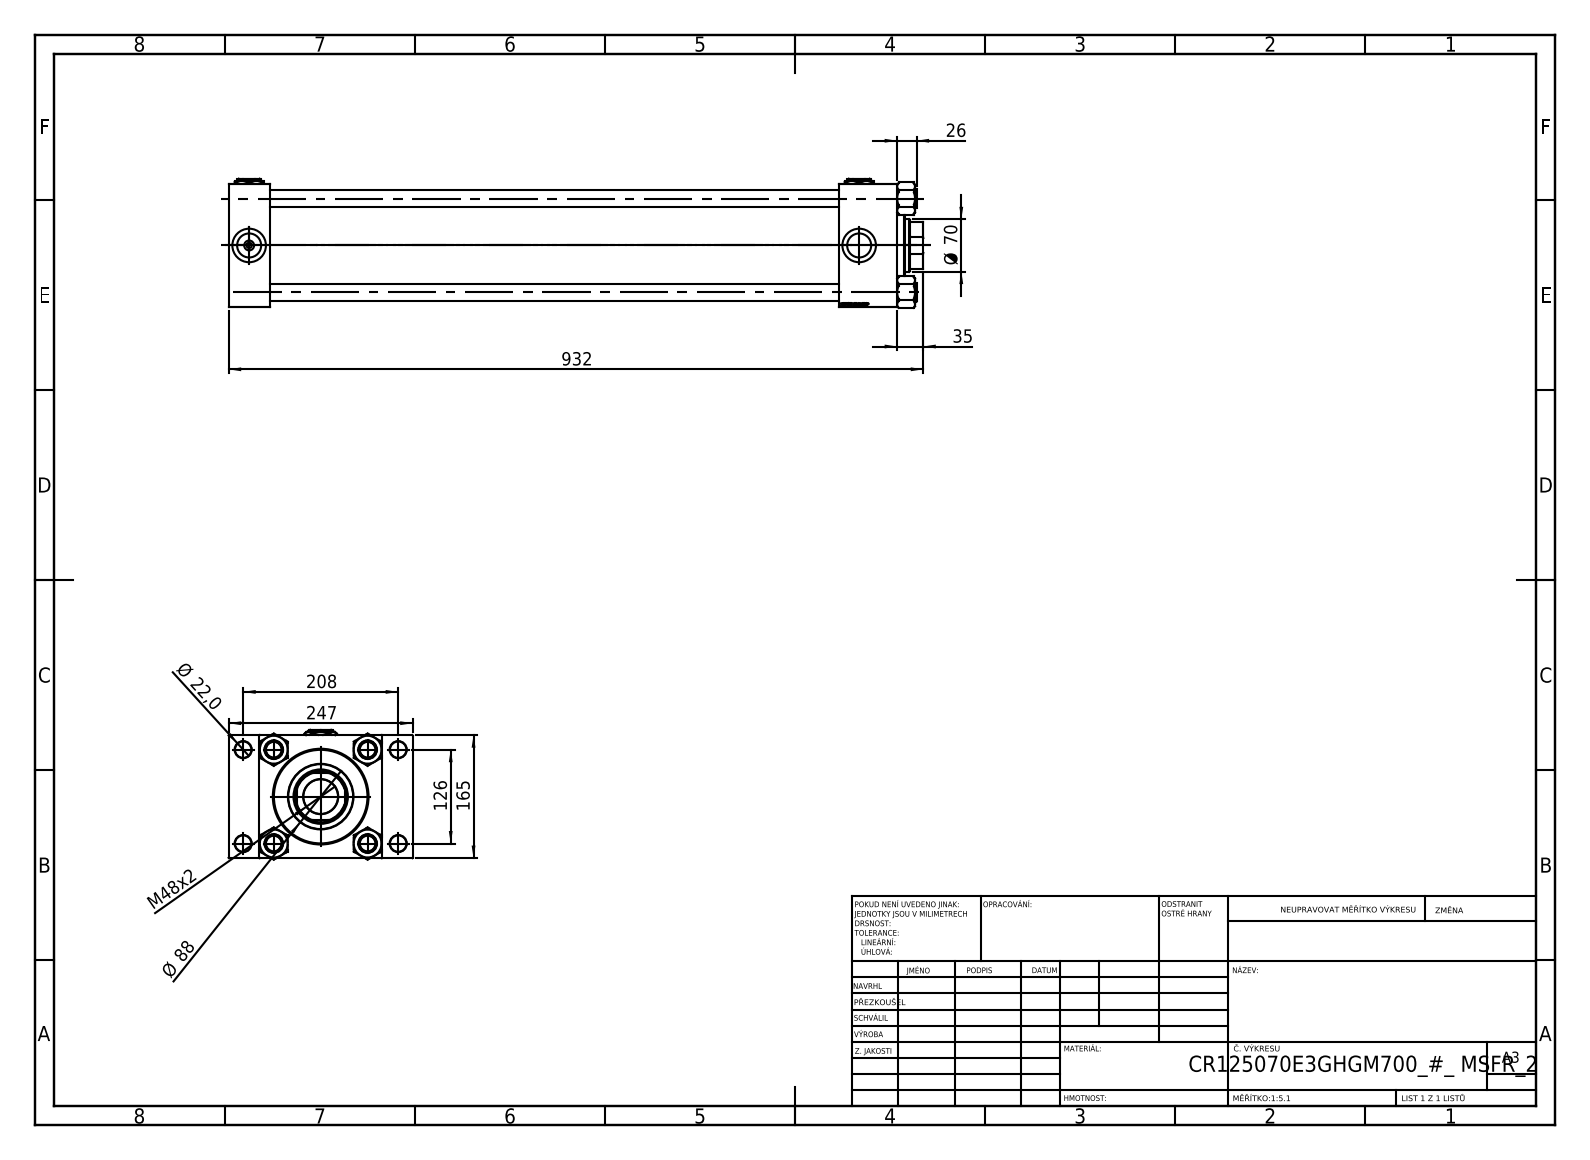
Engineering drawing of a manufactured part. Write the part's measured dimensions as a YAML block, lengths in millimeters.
part_name: "V215CR_VCP_E; V215CR_TYCINKA_E; NUT_M5_E; V215_VC_A (+2 more)"
step_written_by: "SolidWorks 2019 (CONFIG_CONTROL_DESIGN)"
units: millimeters
bodies: {solids: 13, faces: 1284, planar: 593, cylindrical: 97, other: 594}
overall_size: [932, 247, 174.07]
volume: 9729000
surface_area: 1475000
round_holes:
  - {diameter: 22, count: 8}
  - {diameter: 32.24, count: 4}
  - {diameter: 45, count: 4}
  - {diameter: 7, count: 3}
  - {diameter: 46.5, count: 1}
  - {diameter: 70, count: 1}
  - {diameter: 73, count: 1}
  - {diameter: 96, count: 1}
  - {diameter: 125, count: 1}
  - {diameter: 125.5, count: 1}
round_bosses_or_shafts:
  - {diameter: 25, count: 4}
  - {diameter: 131, count: 1}
  - {diameter: 88, count: 1}
partial_cylinders:
  - {radius: 34, count: 1}
face_to_face_distances: [55, 165, 897, 842, 41, 78, 819, 764, 206, 868.3]
hole_center_spacings: [41.05, 89.02, 121.59, 125.9, 132.47, 166.95, 209.13, 126]
